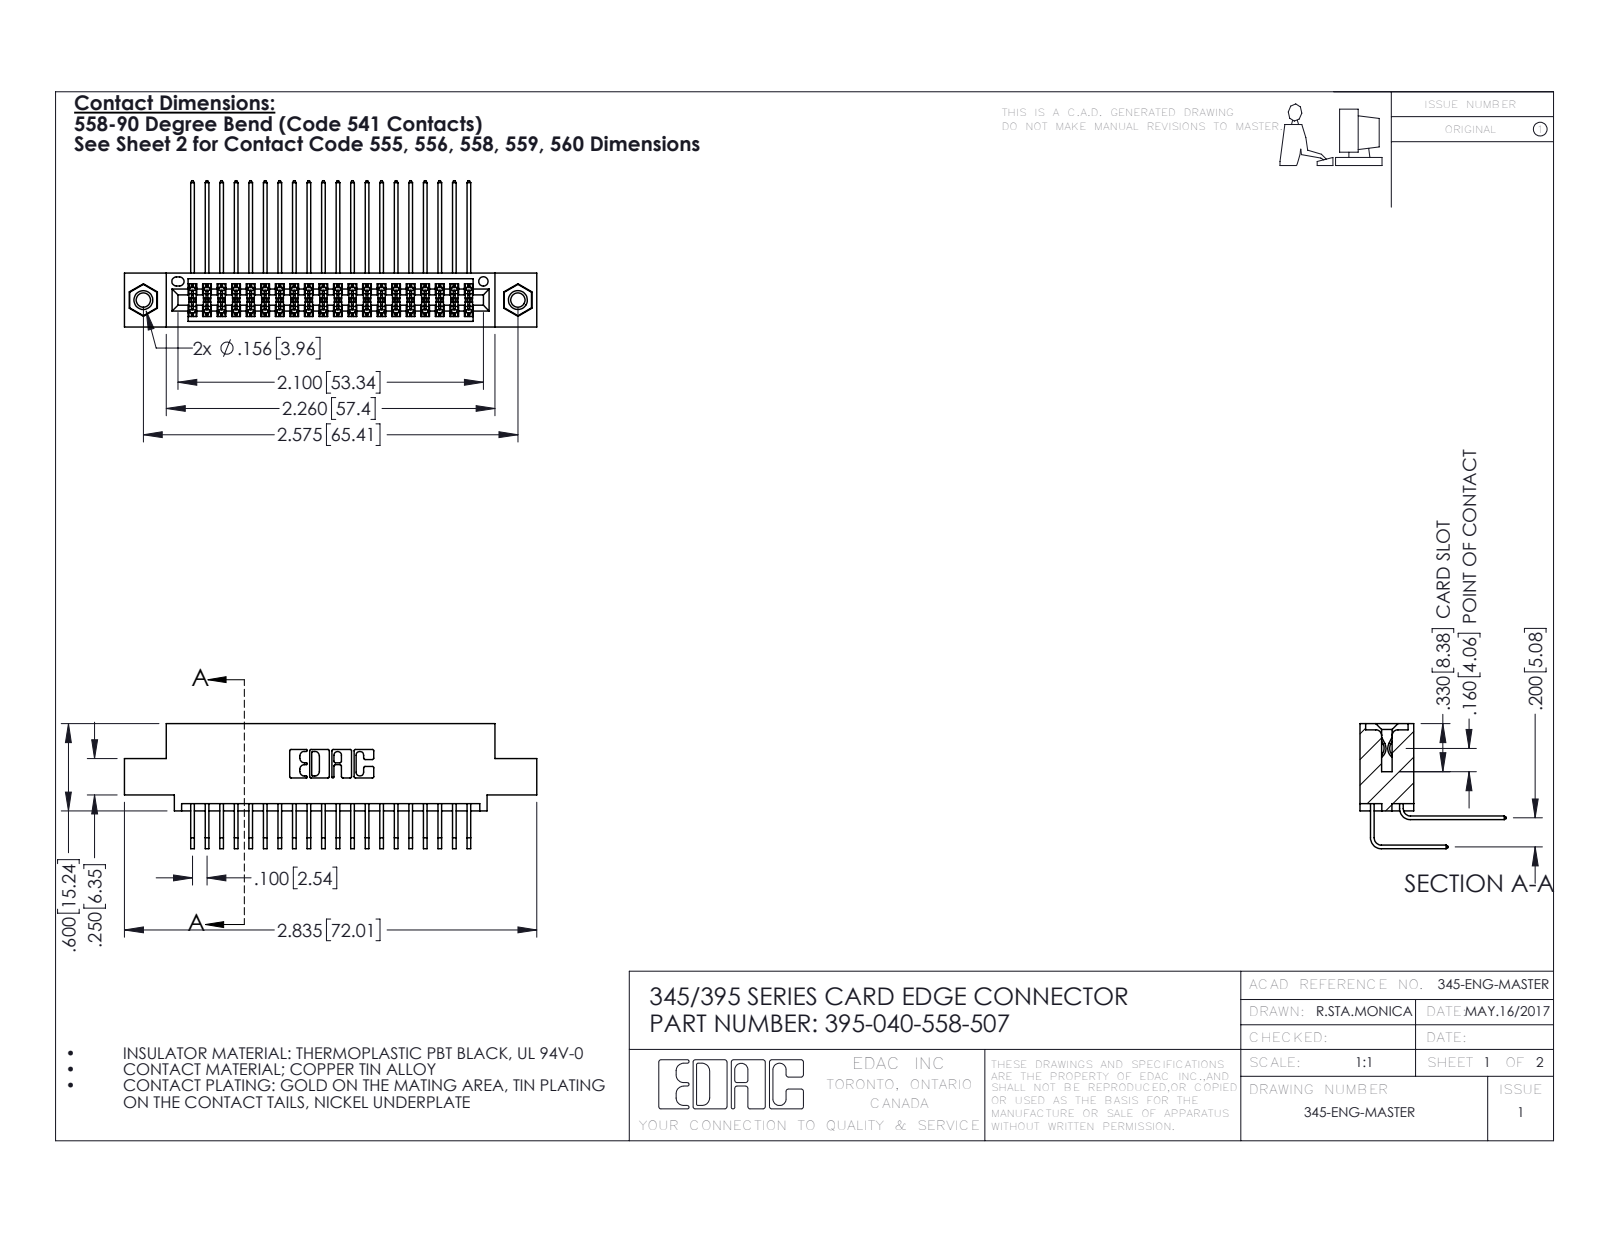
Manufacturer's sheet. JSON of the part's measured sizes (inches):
{"part_name": "345-250-001_345-250-005-103; 345 Part_0.110 Offset - 0.156 Dia-TI; 345-292-001_558 559 Tail - 1; 395-040-558-507 (+1 more)", "step_written_by": "SolidWorks 2016 (CONFIG_CONTROL_DESIGN)", "units": "inches", "bodies": {"solids": 43, "faces": 2270, "planar": 1516, "cylindrical": 738, "other": 16}, "overall_size": [2.835, 1.005, 0.859], "volume_in3": 0.423, "surface_area_in2": 17.1, "round_holes": [[0.098, 2], [0.125, 2], [0.156, 2], [0.064, 1]], "round_bosses_or_shafts": [[0.155, 2]], "partial_cylinders_radius": [[0.006, 61], [0.01, 22], [0.007, 6], [0.031, 6], [0.026, 3], [0.014, 2], [0.019, 2], [0.022, 2]], "face_to_face_distances": [0.2, 0.072, 0.298, 0.37, 0.098, 0.272, 0.025, 0.225, 0.025, 0.175], "hole_center_spacings": [0.27, 2.341, 2.575]}
